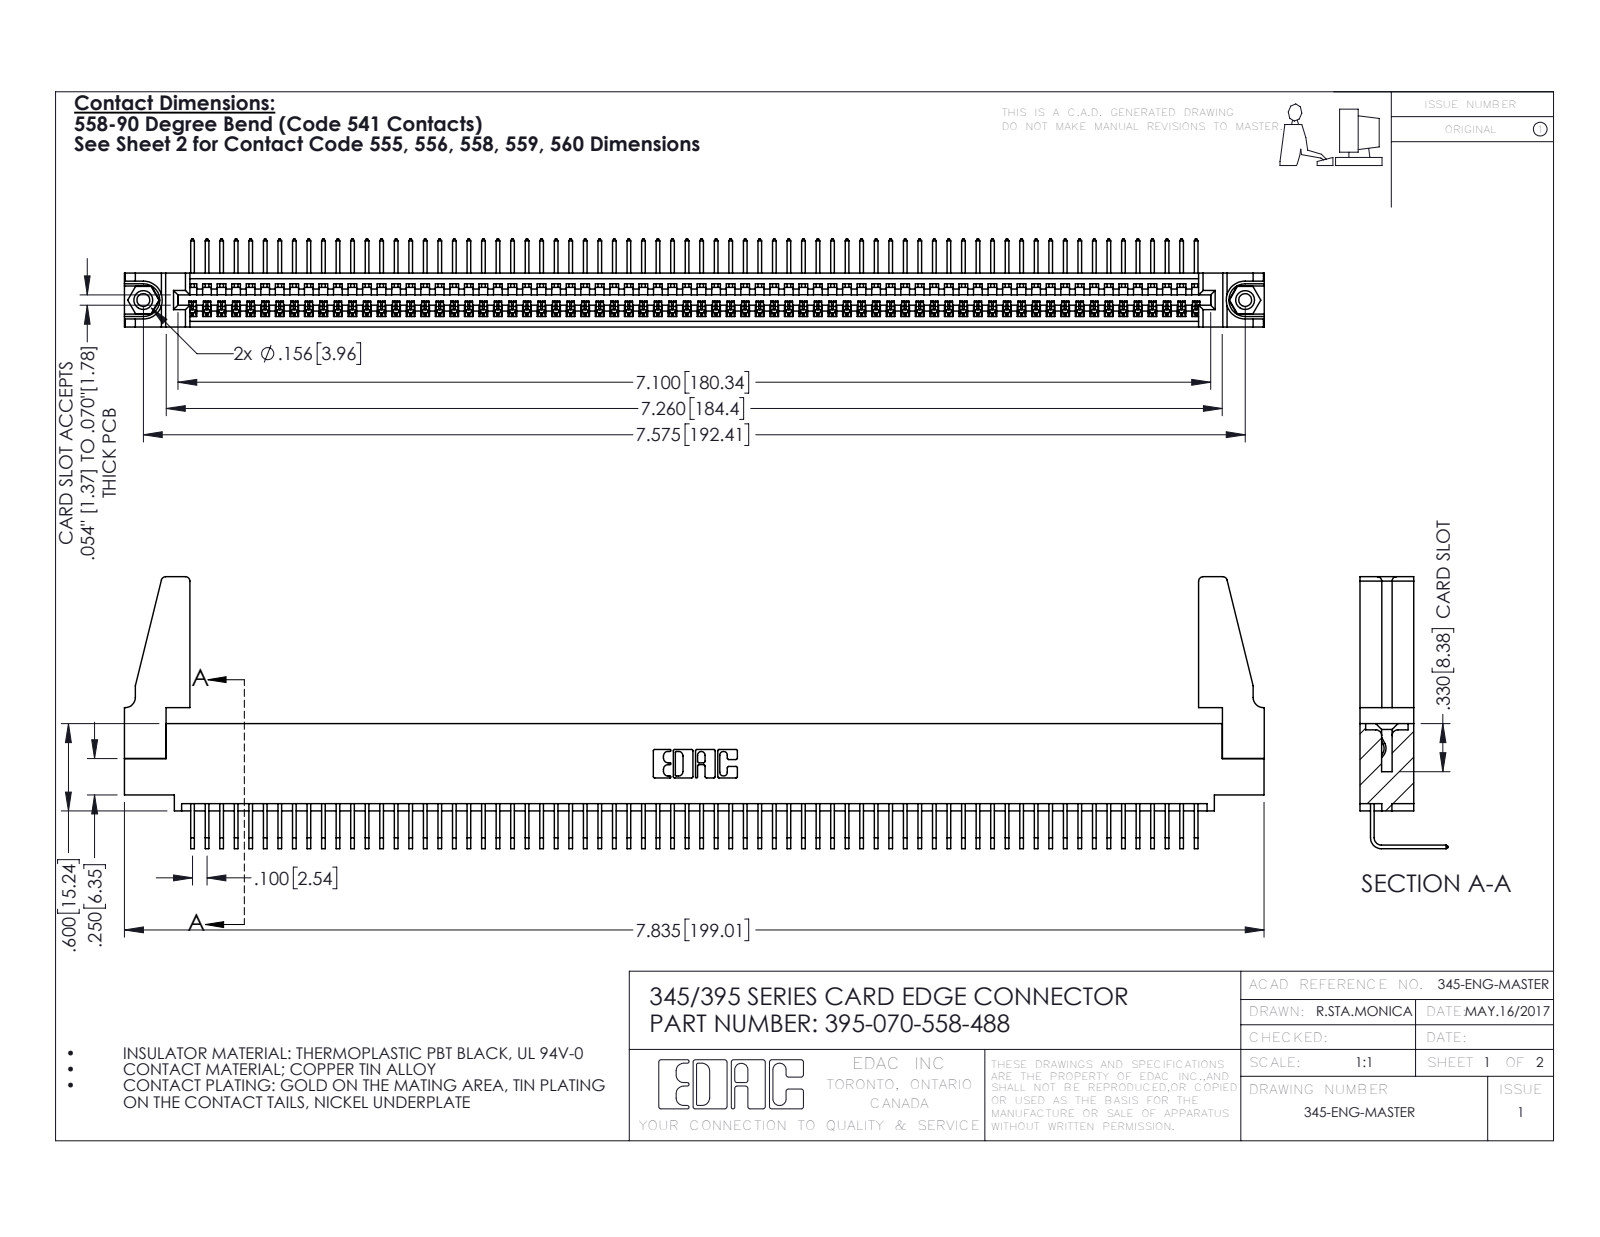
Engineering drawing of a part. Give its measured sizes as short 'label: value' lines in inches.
name: 345-250-001_345-250-001-102; 345 Part_0.110 Offset - 0.156 Dia-TH; 395-070-558-488; 345-220-078_345-220-088 (+1 more)
written by: SolidWorks 2016 (CONFIG_CONTROL_DESIGN)
unit: in
bodies: 75 solids, 4454 faces (3096 planar, 1342 cylindrical, 16 other)
size: 7.836 × 1.869 × 0.605
volume: 1.376 in³; area: 47.43 in²
holes: 2× ⌀0.089, 2× ⌀0.125, 2× ⌀0.156, 1× ⌀0.064
bosses: 2× ⌀0.155
rounds: 140× R0.006, 22× R0.01, 8× R0.03, 6× R0.007, 6× R0.031, 3× R0.026, 2× R0.031, 2× R0.04
face distances: 0.072, 0.298, 0.37, 0.2, 0.098, 0.272, 0.025, 0.225, 0.149, 0.072
hole spacings: 0.27, 7.339, 7.575
